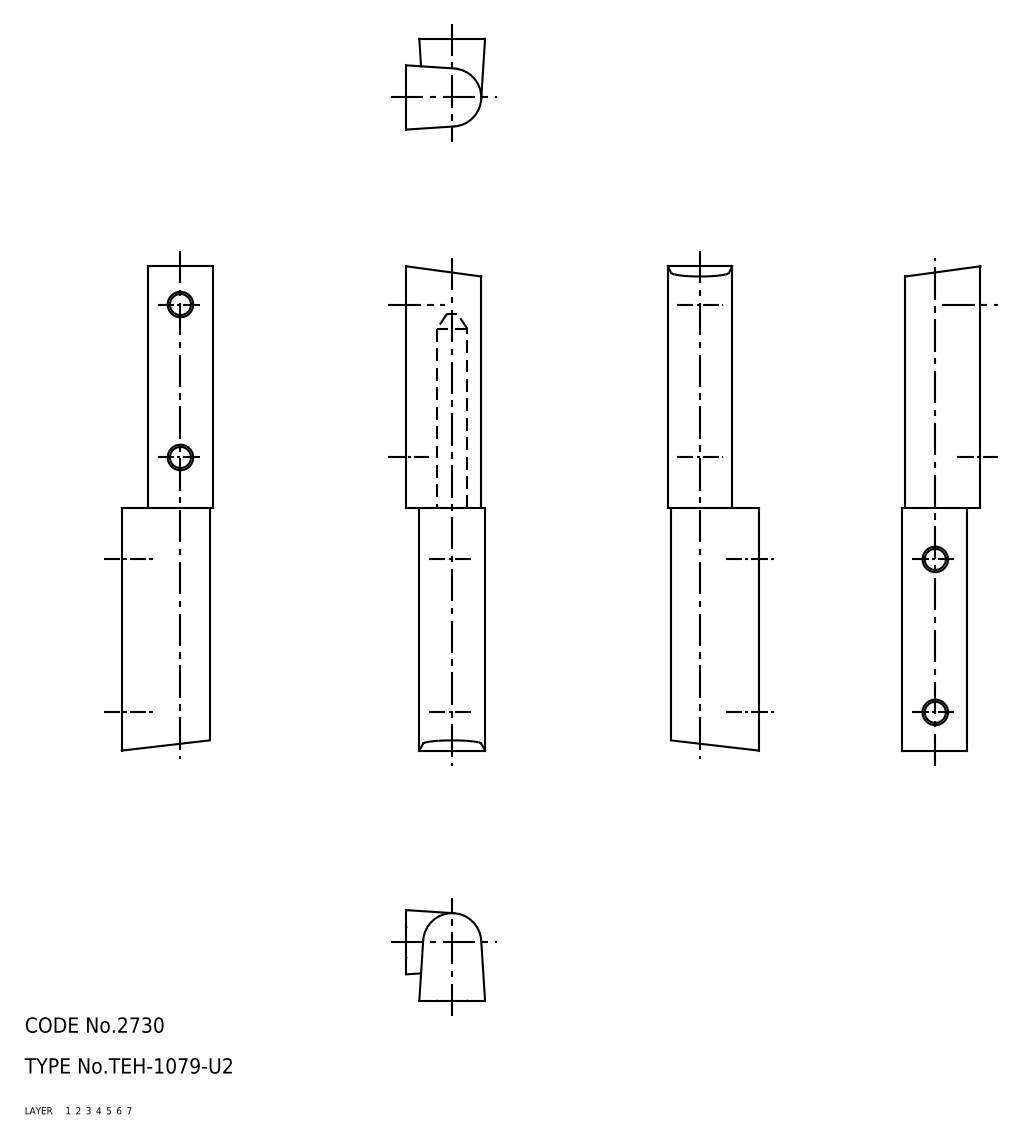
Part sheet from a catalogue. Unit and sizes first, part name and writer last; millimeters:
Units: millimetres
Overall size (bounding box): 95 × 17.8 × 15.45
Volume: 15 598 mm³ · Surface area: 8 890 mm²
Bodies: 3 solids, 36 faces (0 planar, 0 cylindrical, 36 other)
Part name (STEP PRODUCT): shaft; hinge pieces_B; hinge pieces_A; TEH_1079_U2_5564_36
STEP written by: CADfix (AUTOMOTIVE_DESIGN)
